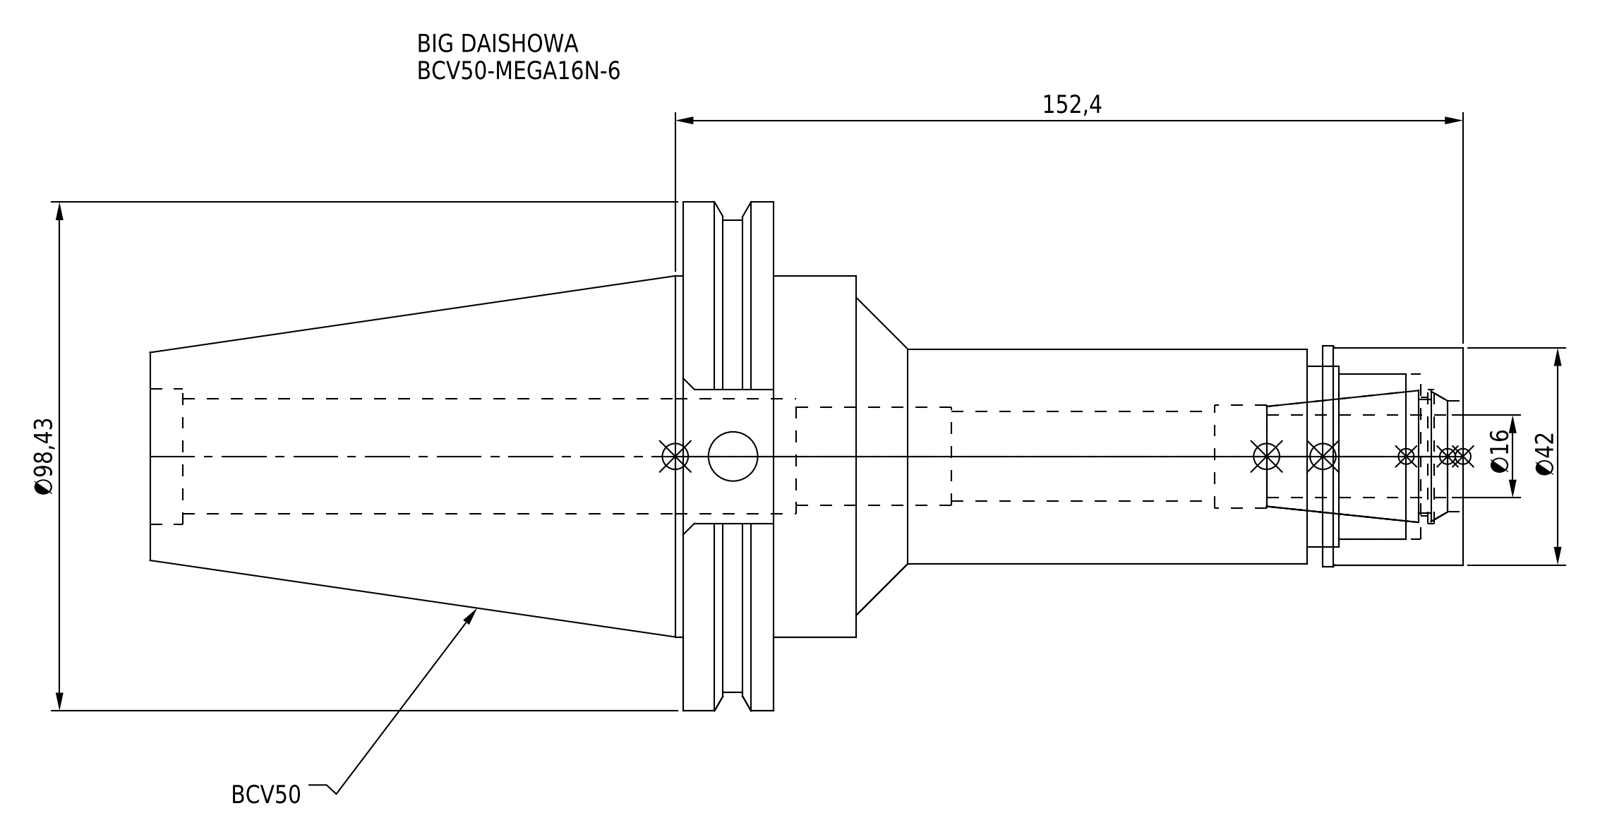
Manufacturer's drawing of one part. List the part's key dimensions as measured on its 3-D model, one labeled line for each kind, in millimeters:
Part name (STEP PRODUCT): BCV50-MEGA16N-6_1.stp; BCV50MN16060-160_ASM.stp; BCV50-MEGA16N-6-160.stp; MGN16_1.stp (+3 more)
STEP written by: SolidWorks 2019 (CONFIG_CONTROL_DESIGN)
Units: millimetres
Bodies: 2 solids, 91 faces (33 planar, 44 cylindrical, 14 other)
Overall size (bounding box): 254 × 98.42 × 94.95
Volume: 508 897 mm³ · Surface area: 76 473 mm²
Round holes (diameter × count): ⌀9.53 ×1, ⌀17.3 ×1, ⌀19 ×1, ⌀20 ×1, ⌀21.5 ×1, ⌀22.3 ×1, ⌀23 ×1, ⌀26 ×1, ⌀26.23 ×1, ⌀32 ×1, ⌀35 ×1
Round bosses / shafts (diameter × count): ⌀98.42 ×1, ⌀91.29 ×1, ⌀69.85 ×1, ⌀42.7 ×1, ⌀42 ×1, ⌀41.5 ×1
Main face-to-face distances: 17.55, 133.35, 150.9, 117.4, 15.95, 33.5, 254, 136.6, 120.65, 103.1
